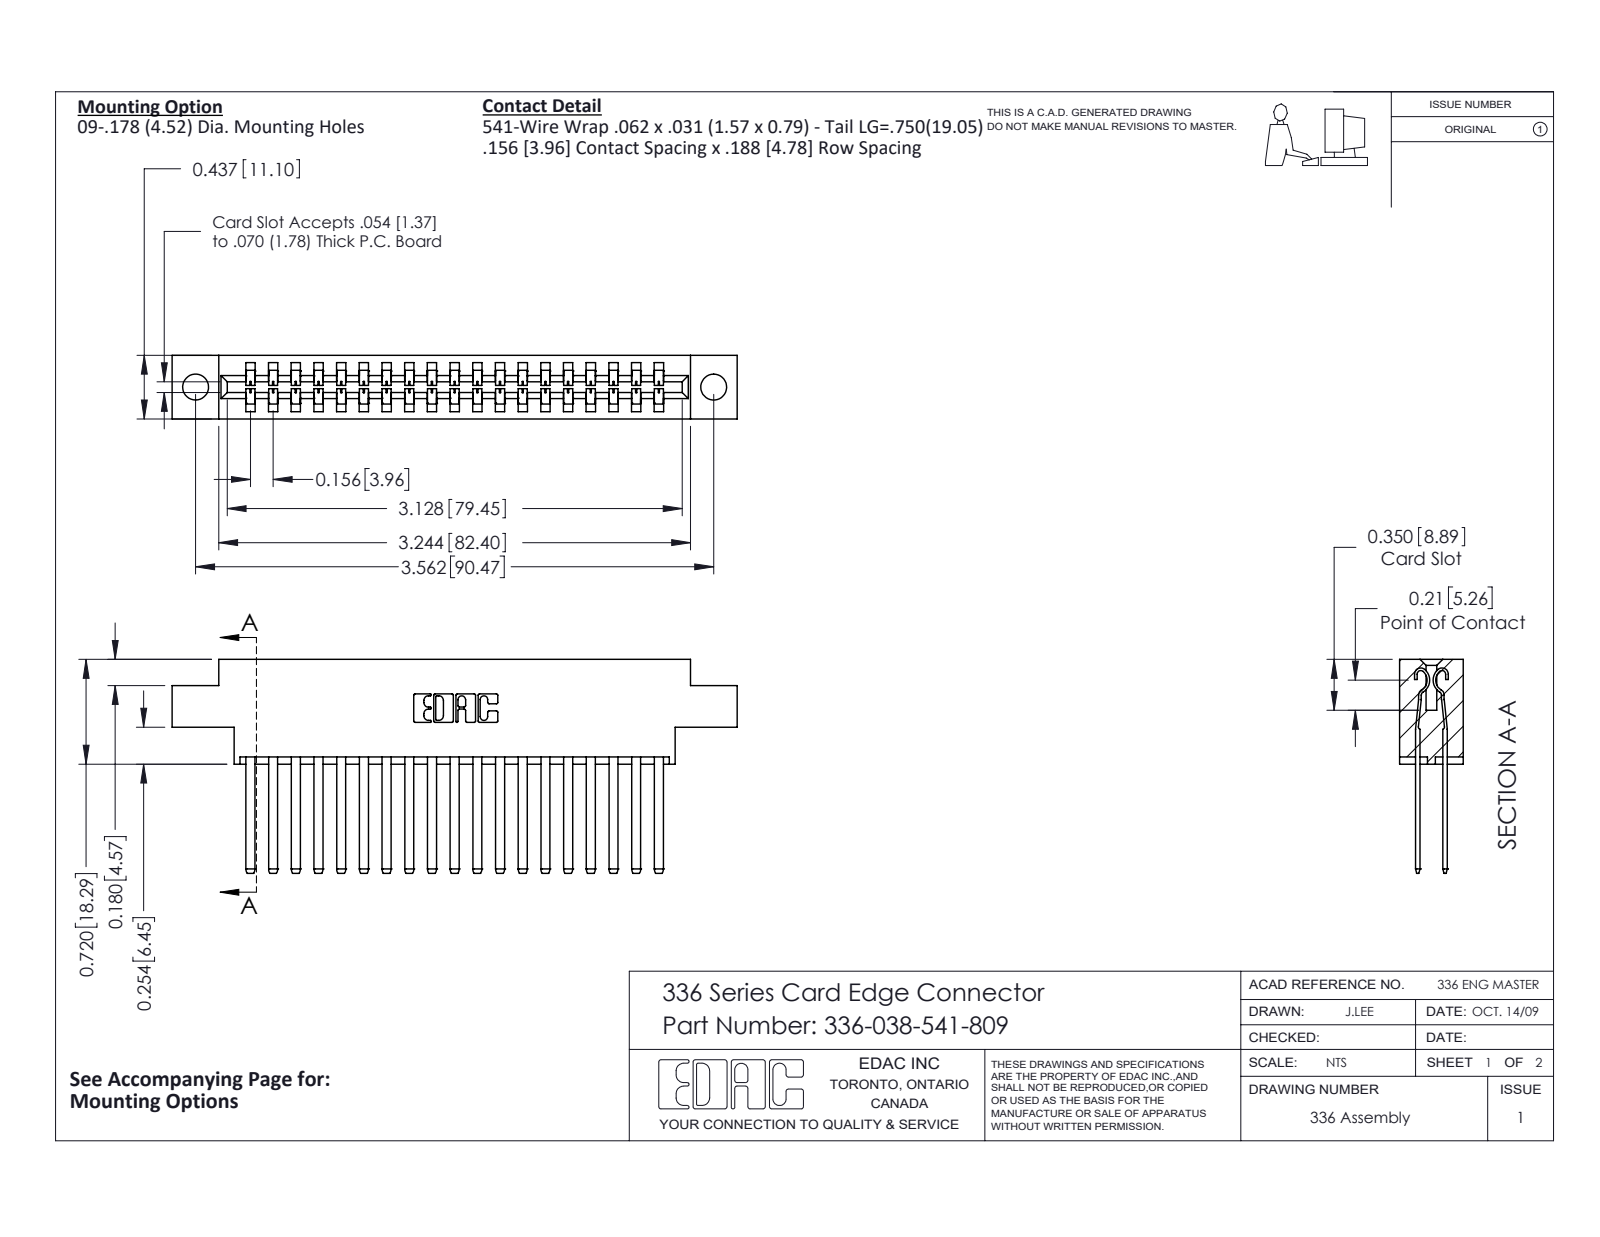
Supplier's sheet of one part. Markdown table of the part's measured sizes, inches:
| quantity | value |
| --- | --- |
| part name | 336-290-001_336-290-541; 336-038-541-809; 336 Part_Offset - .178 Dia - TH |
| STEP written by | SolidWorks 2020 (CONFIG_CONTROL_DESIGN) |
| units | inches |
| bodies | 39 solids, 1714 faces (1062 planar, 652 cylindrical, 0 other) |
| overall size | 3.885 × 1.47 × 0.437 |
| volume | 0.875 in³ |
| surface area | 27.64 in² |
| round holes (diameter × count) | 0.178 × 2 |
| partial cylindrical surfaces (radius × count) | 0.004 × 76, 0.056 × 38, 0.01 × 22, 0.007 × 6, 0.031 × 6, 0.022 × 4, 0.04 × 4, 0.026 × 3 |
| main face-to-face distances | 0.188, 0.328, 0.14, 0.297, 0.109, 0.031, 0.437, 0.033, 0.181, 0.256 |
| hole center spacings | 3.562 |
